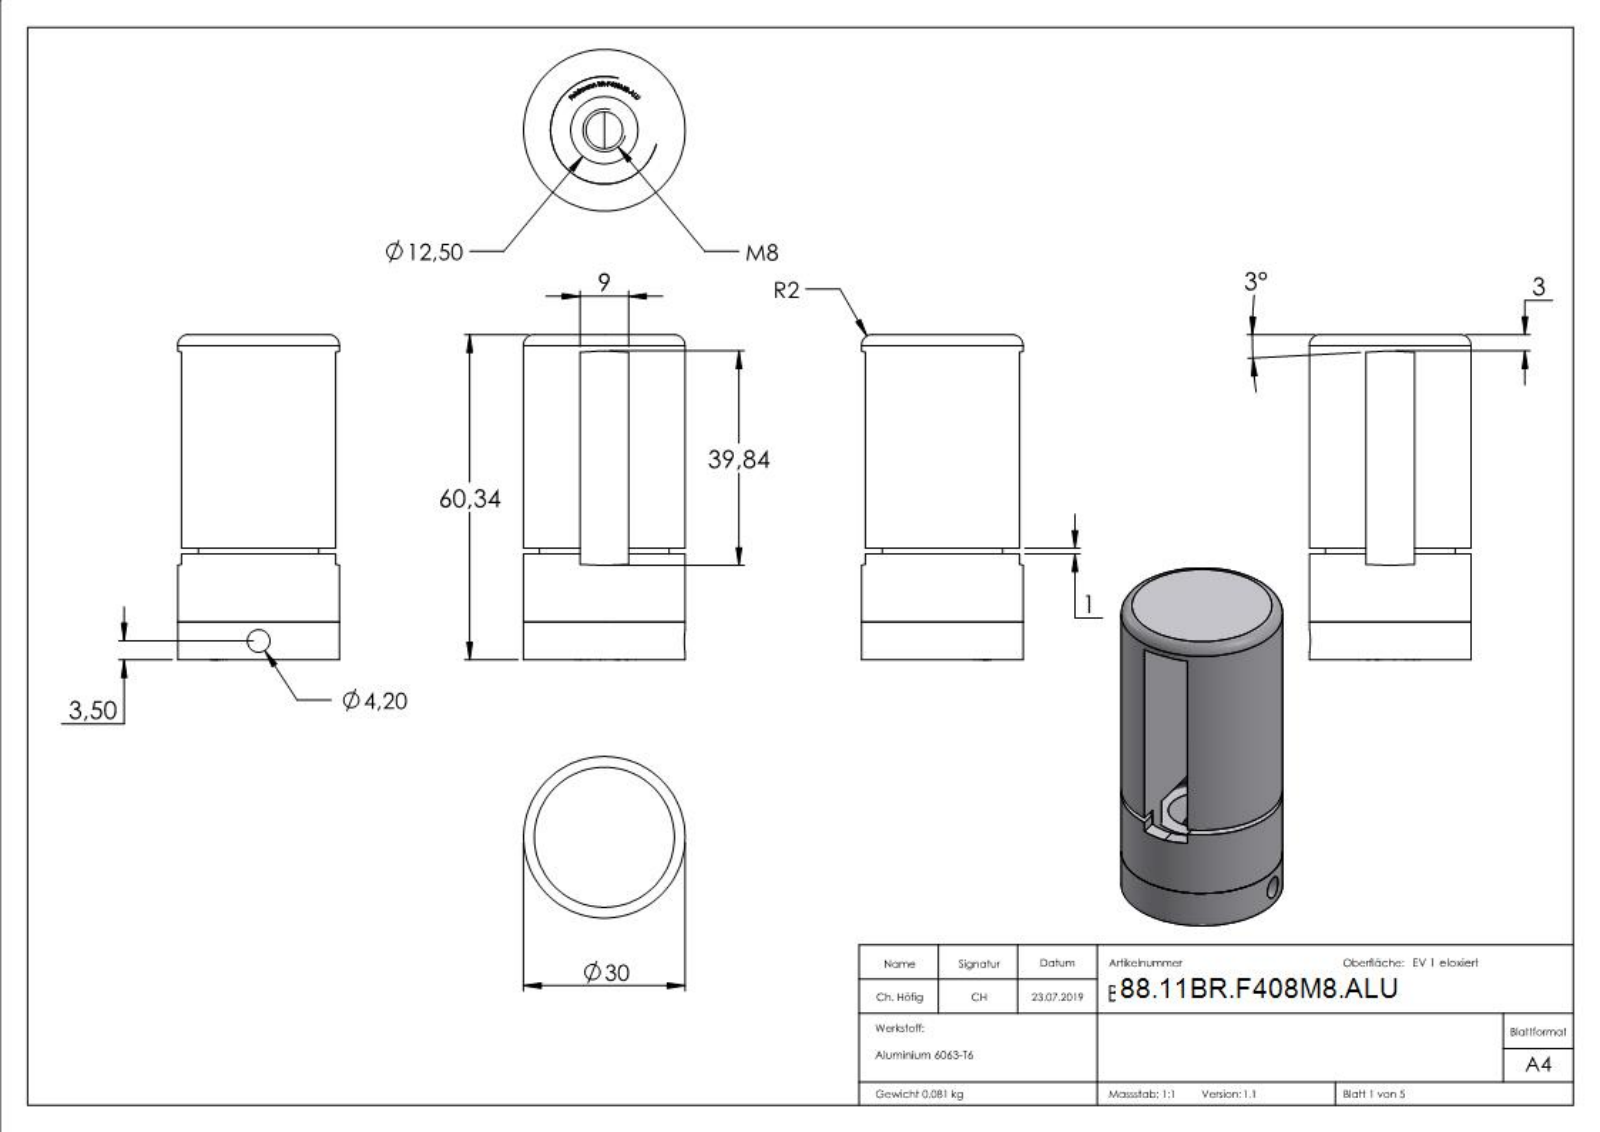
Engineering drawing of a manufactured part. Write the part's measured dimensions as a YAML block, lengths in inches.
part_name: "BR-R1XM8-XXX Teil1; BR-R1XM8-XXX Teil3; BR-R1XM8-XXX Teil2_BR-F408M8-ALU Teil2; BR-F408M8-ALU (+3 more)"
step_written_by: "SolidWorks 2015 (CONFIG_CONTROL_DESIGN)"
units: inches
bodies: {solids: 3, faces: 329, planar: 195, cylindrical: 12, other: 122}
overall_size: [2.533, 1.181, 1.181]
volume: 1.822
surface_area: 20.78
round_holes:
  - {diameter: 0.165, count: 1}
  - {diameter: 0.268, count: 1}
  - {diameter: 0.492, count: 1}
  - {diameter: 0.953, count: 1}
round_bosses_or_shafts:
  - {diameter: 1.181, count: 1}
  - {diameter: 0.787, count: 1}
partial_cylinders:
  - {radius: 0.344, count: 1}
  - {radius: 0.474, count: 1}
face_to_face_distances: [0.354, 0.276, 2.376, 2.1, 0.039, 0.5, 0.815, 0.539, 1.561, 0.315]
